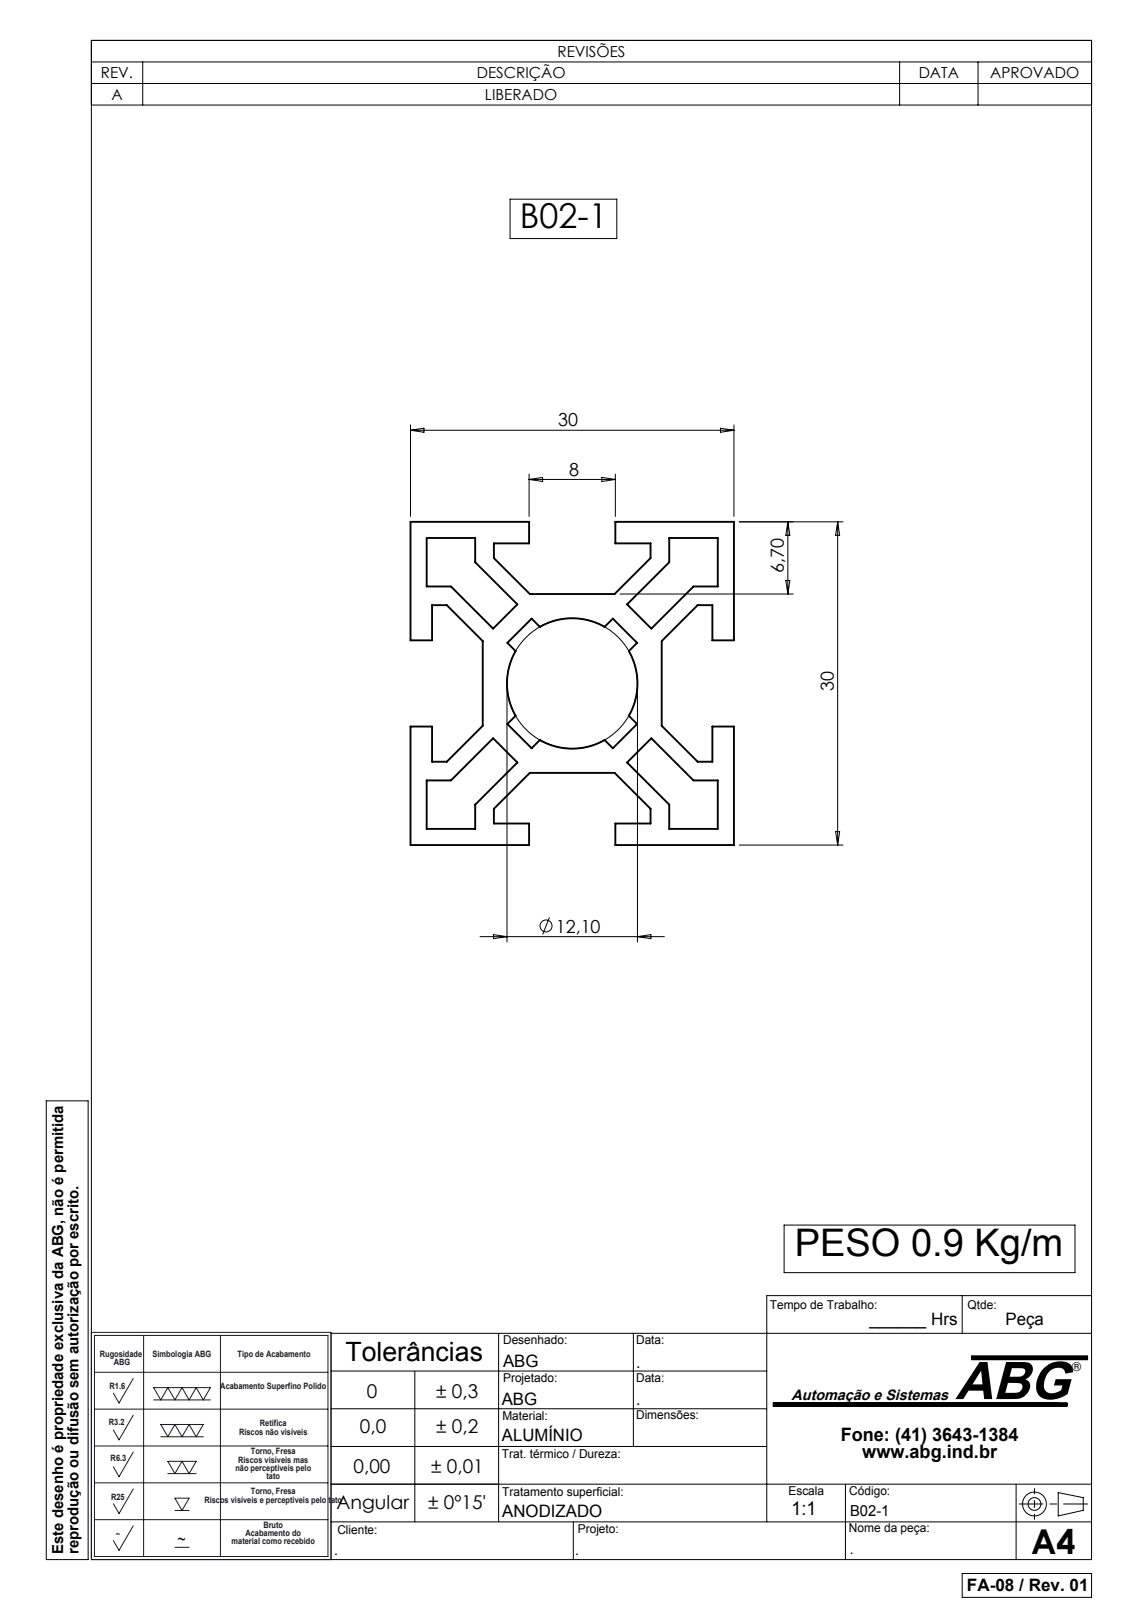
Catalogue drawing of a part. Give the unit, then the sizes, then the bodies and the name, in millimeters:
Units: millimetres
Overall size (bounding box): 6000 × 30 × 30
Partial cylindrical surfaces — rounded edges, fillets, slot ends (radius × count): R6.05 ×1
Main face-to-face distances: 1.5, 30, 4.68, 28.5, 23.3, 21.8, 6.7, 5.2, 3.18, 2
Volume: 2 034 000 mm³ · Surface area: 2 207 000 mm²
Bodies: 1 solid, 91 faces (86 planar, 5 cylindrical, 0 other)
Part name (STEP PRODUCT): B02-1
STEP written by: SolidWorks 2007 (CONFIG_CONTROL_DESIGN)
